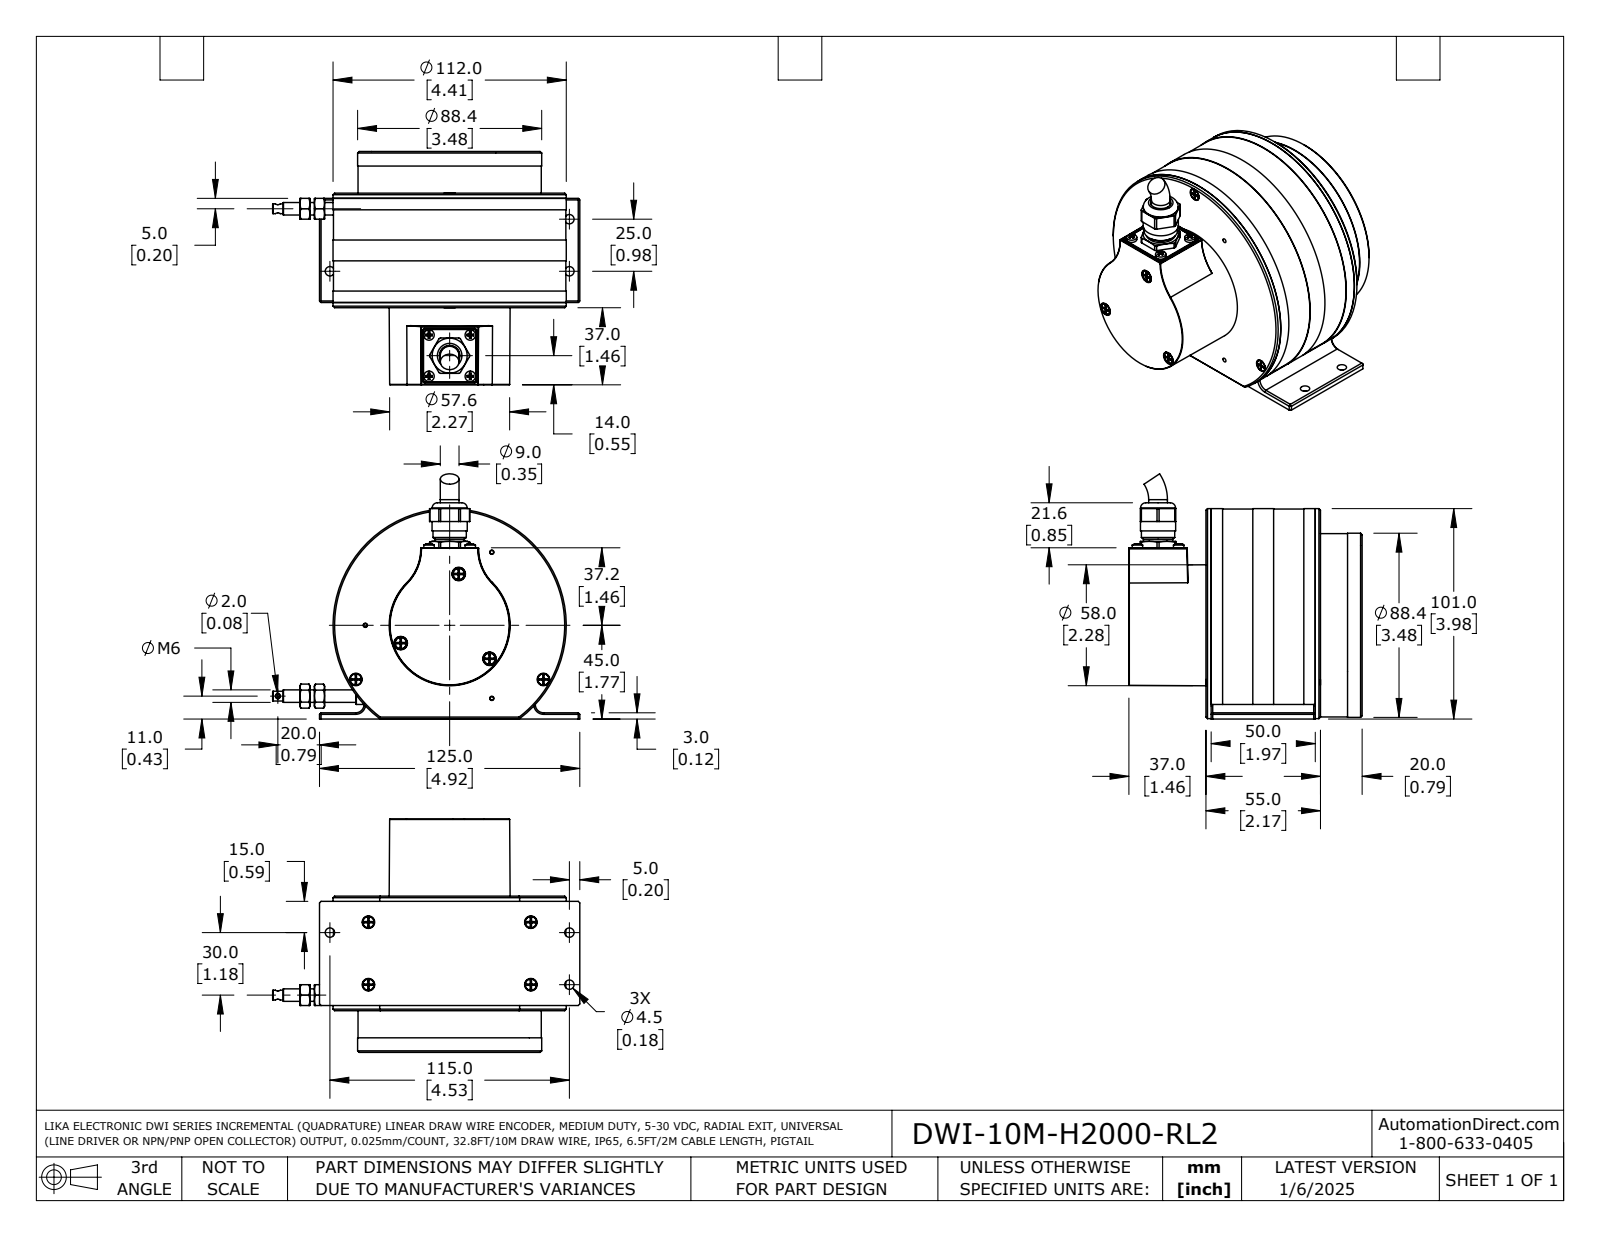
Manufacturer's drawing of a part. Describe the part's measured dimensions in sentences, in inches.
The part is named "DWI-10M-H2000-RL2". Its 3-D file was written by "SolidWorks 2021 (AUTOMOTIVE_DESIGN)". It is 35 solids with 2198 faces: 1264 planar, 494 cylindrical and 440 other. Overall it measures 5.807 by 4.634 by 4.409 inches. Its volume is 17.02 cubic inches and its surface area 231.6 square inches. Round holes: 13 of diameter 0.098, 7 of diameter 0.126, 7 of diameter 0.236, 4 of diameter 0.157, 4 of diameter 0.177, 4 of diameter 0.197, 3 of diameter 0.081, 3 of diameter 0.11, 2 of diameter 0.059, 2 of diameter 0.063, 2 of diameter 0.079, 2 of diameter 0.315. Round bosses or shafts: 12 of diameter 0.053, 12 of diameter 0.031, 11 of diameter 0.118, 7 of diameter 0.098, 4 of diameter 0.197, 1 of diameter 4.409, 1 of diameter 3.48, 1 of diameter 3.465. Partial cylindrical surfaces (rounded edges, fillets, slot ends): 48 of radius 0.008, 42 of radius 0.007, 6 of radius 0.02, 6 of radius 0.039, 5 of radius 0.03, 2 of radius 0.157, 1 of radius 0.098, 1 of radius 0.161. The main face-to-face distances are 0.079, 0.787, 0.02, 0.098, 0.807, 2.067, 1.772, 1.752, 0.394, 2.146. The hole center spacings are 0.984, 1.705, 0.648, 0.728, 0.509, 0.827, 1.039, 1.091.
